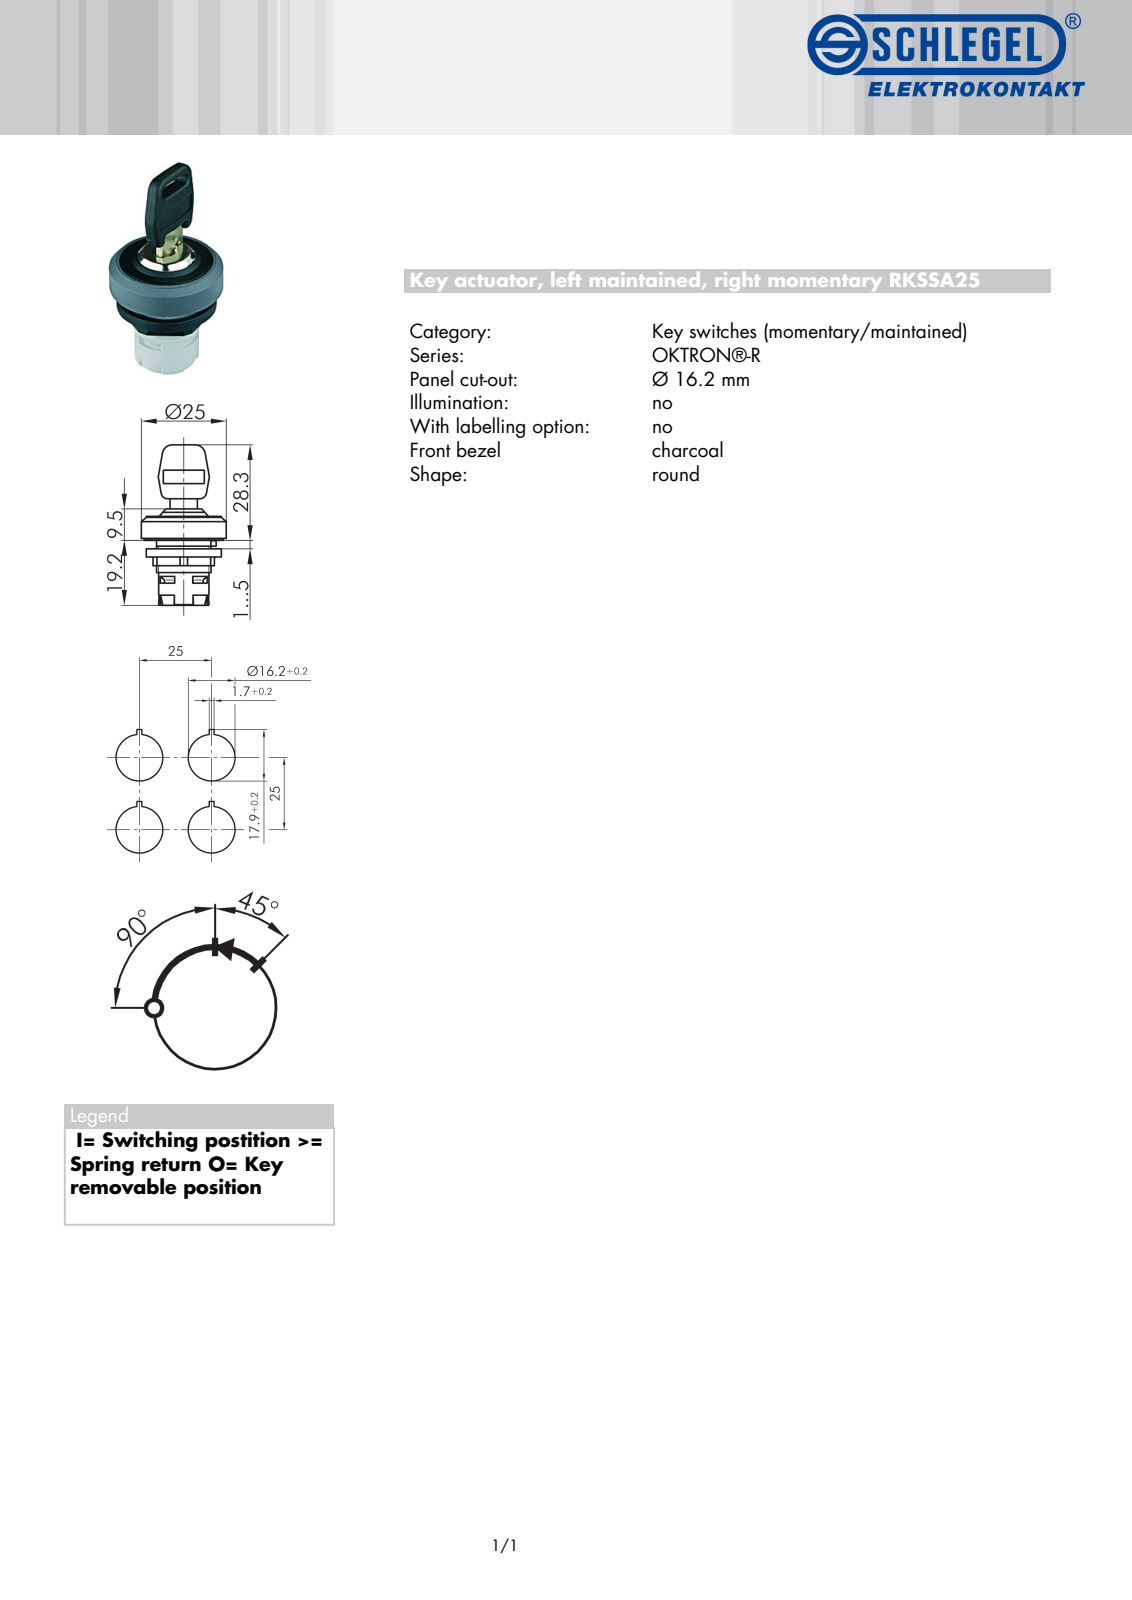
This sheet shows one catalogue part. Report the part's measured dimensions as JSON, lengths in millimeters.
{"part_name": "RKSSA..._vereinfacht", "step_written_by": "Autodesk Inventor 2016 (AUTOMOTIVE_DESIGN)", "units": "millimeters", "bodies": {"solids": 1, "faces": 289, "planar": 142, "cylindrical": 83, "other": 64}, "overall_size": [47.78, 24.9, 24.9], "volume_mm3": 7942, "surface_area_mm2": 5557, "round_holes": [[12.05, 1], [12.65, 1], [14.8, 1], [16.15, 1], [16.5, 1], [17.6, 1], [19.5, 1], [20.03, 1]], "round_bosses_or_shafts": [[24.9, 1], [23, 1], [22, 1], [21.47, 1], [19.67, 1], [16, 1], [14.65, 1], [12, 1]], "partial_cylinders_radius": [[0.5, 32], [2, 6], [1.25, 2], [6.28, 1], [10.03, 1]], "face_to_face_distances": [5.46, 19.2, 24.66, 3.52, 8.46, 3.5, 26.28, 7.08, 1.62, 19.72]}
